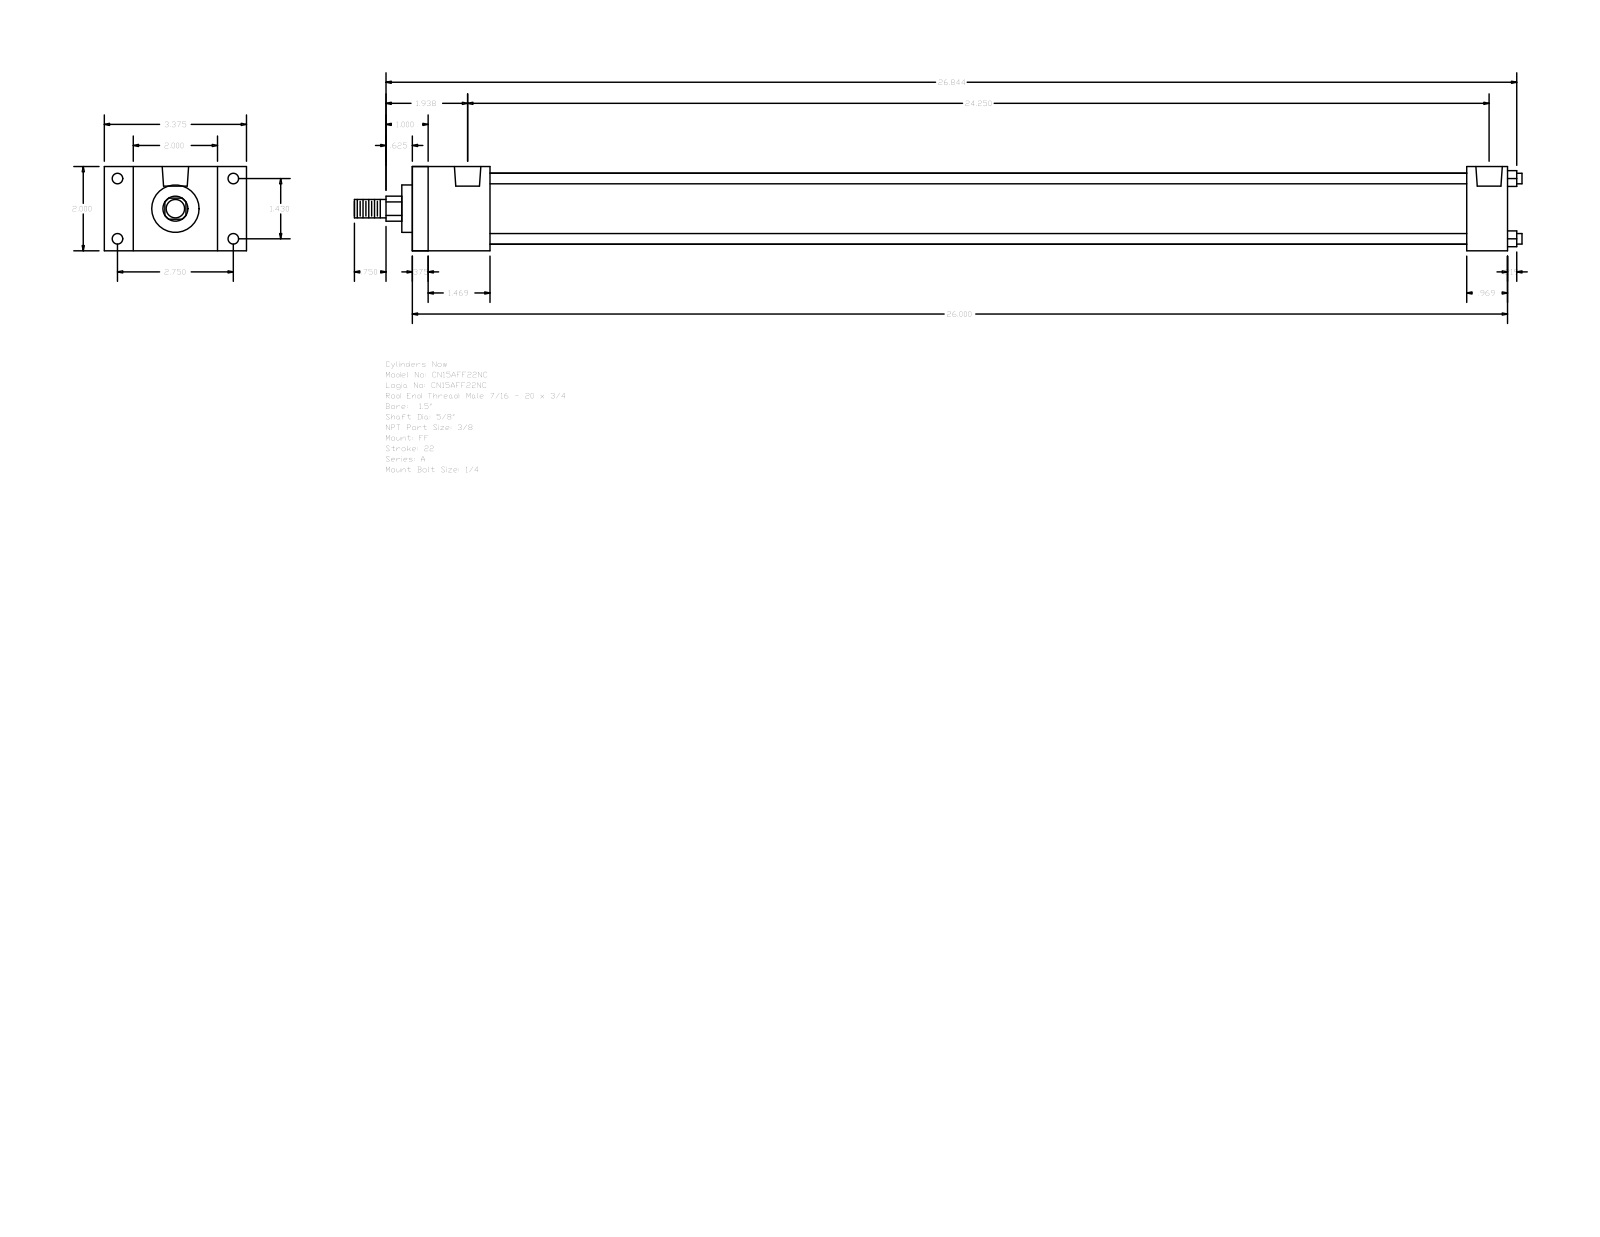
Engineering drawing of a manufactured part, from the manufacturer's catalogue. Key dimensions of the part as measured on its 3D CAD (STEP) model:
Part name (STEP PRODUCT): A_FF__0150_0.625
STEP written by: GSSL Pune (CONFIG_CONTROL_DESIGN)
Units: millimetres
Bodies: 0 solids, 92 faces (64 planar, 28 cylindrical, 0 other)
Overall size (bounding box): 704.06 × 85.72 × 50.8
Round holes (diameter × count): ⌀5.56 ×4, ⌀6.35 ×4, ⌀15.93 ×2
Round bosses / shafts (diameter × count): ⌀6.35 ×4, ⌀42.93 ×1, ⌀28.57 ×1, ⌀15.88 ×1, ⌀11.11 ×1
Partial cylindrical surfaces — rounded edges, fillets, slot ends (radius × count): R7.54 ×1
Main face-to-face distances: 50.8, 660.39, 9.52, 650.87, 46.83, 635.79, 37.31, 626.27, 588.96, 613.56
Hole centre spacings: 3.97, 36.32, 69.84, 78.72, 608.01, 611.98, 615.95
